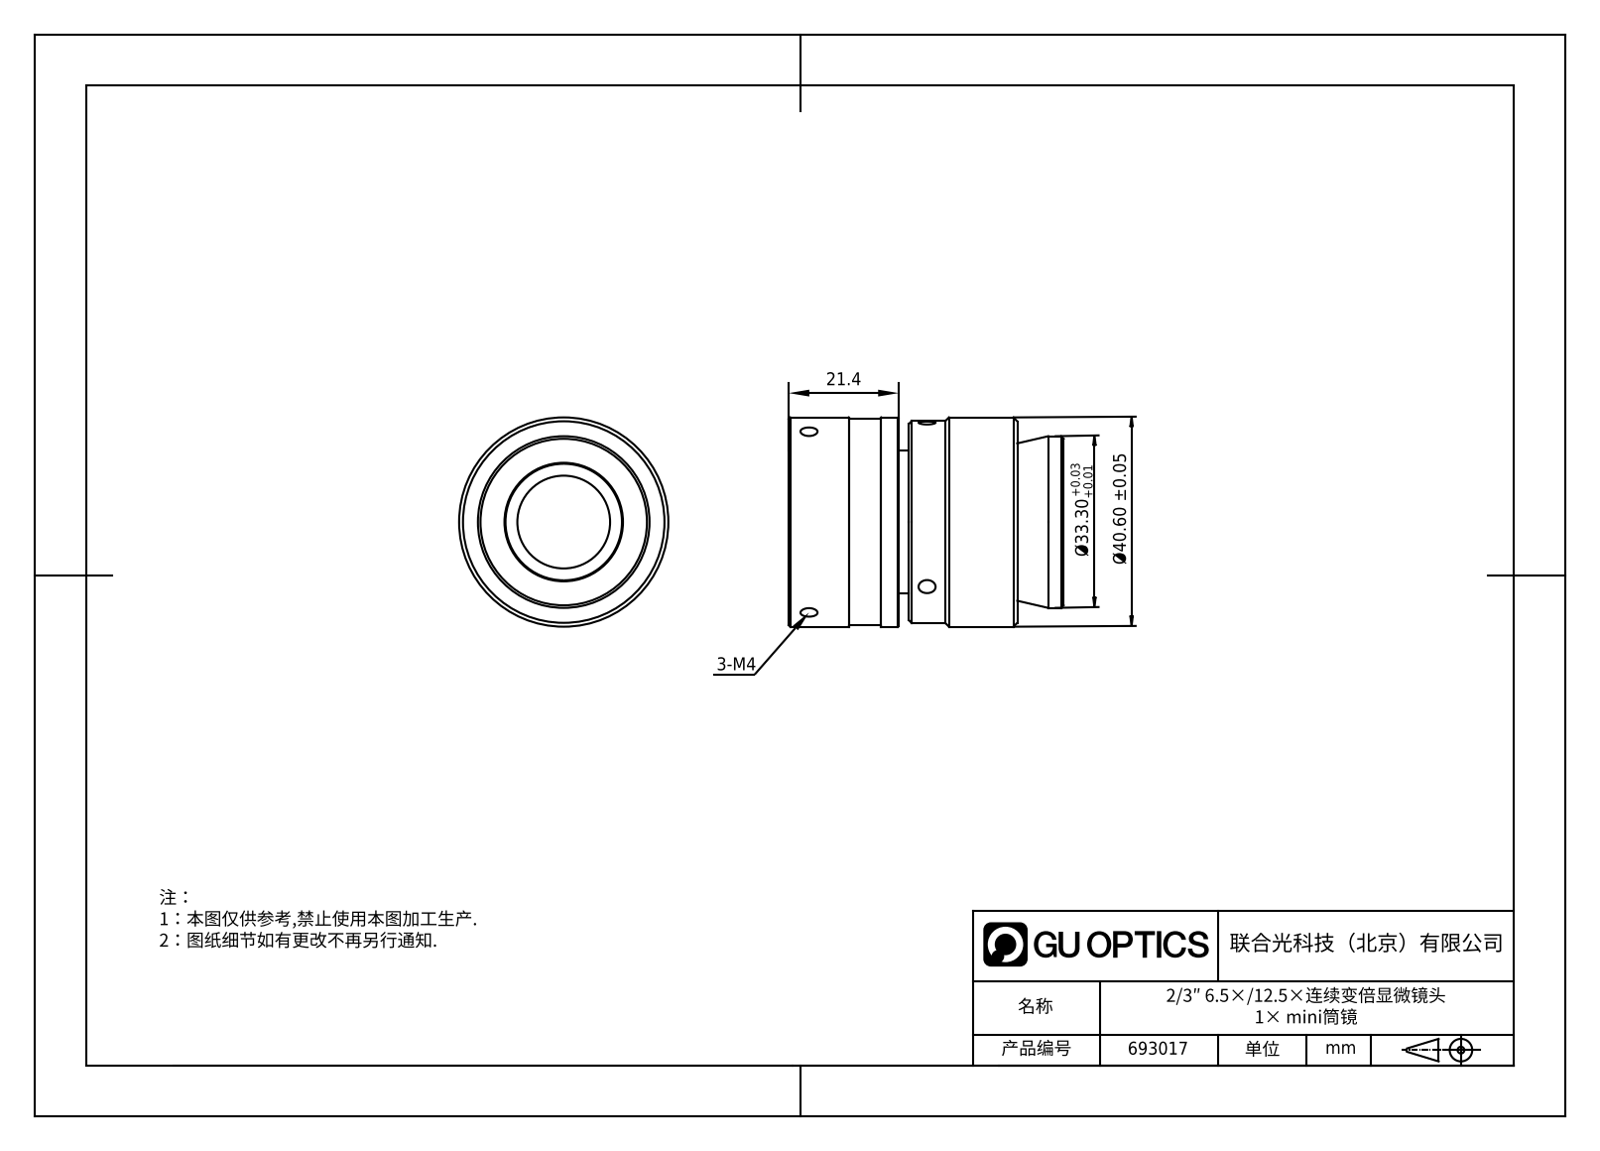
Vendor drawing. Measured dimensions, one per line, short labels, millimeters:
name: 693017
written by: SolidWorks 2020 (CONFIG_CONTROL_DESIGN)
unit: mm
bodies: 0 solids, 37 faces (8 planar, 18 cylindrical, 11 other)
size: 53.35 × 40.6 × 40.6
holes: 6× ⌀3.3, 1× ⌀19.25, 1× ⌀21.25, 1× ⌀23, 1× ⌀33.3
bosses: 1× ⌀40.6, 1× ⌀40, 1× ⌀39.14, 1× ⌀27.82, 1× ⌀18
face distances: 11.79, 13.79, 2, 34.79, 23, 21, 43.79, 32, 30, 9
